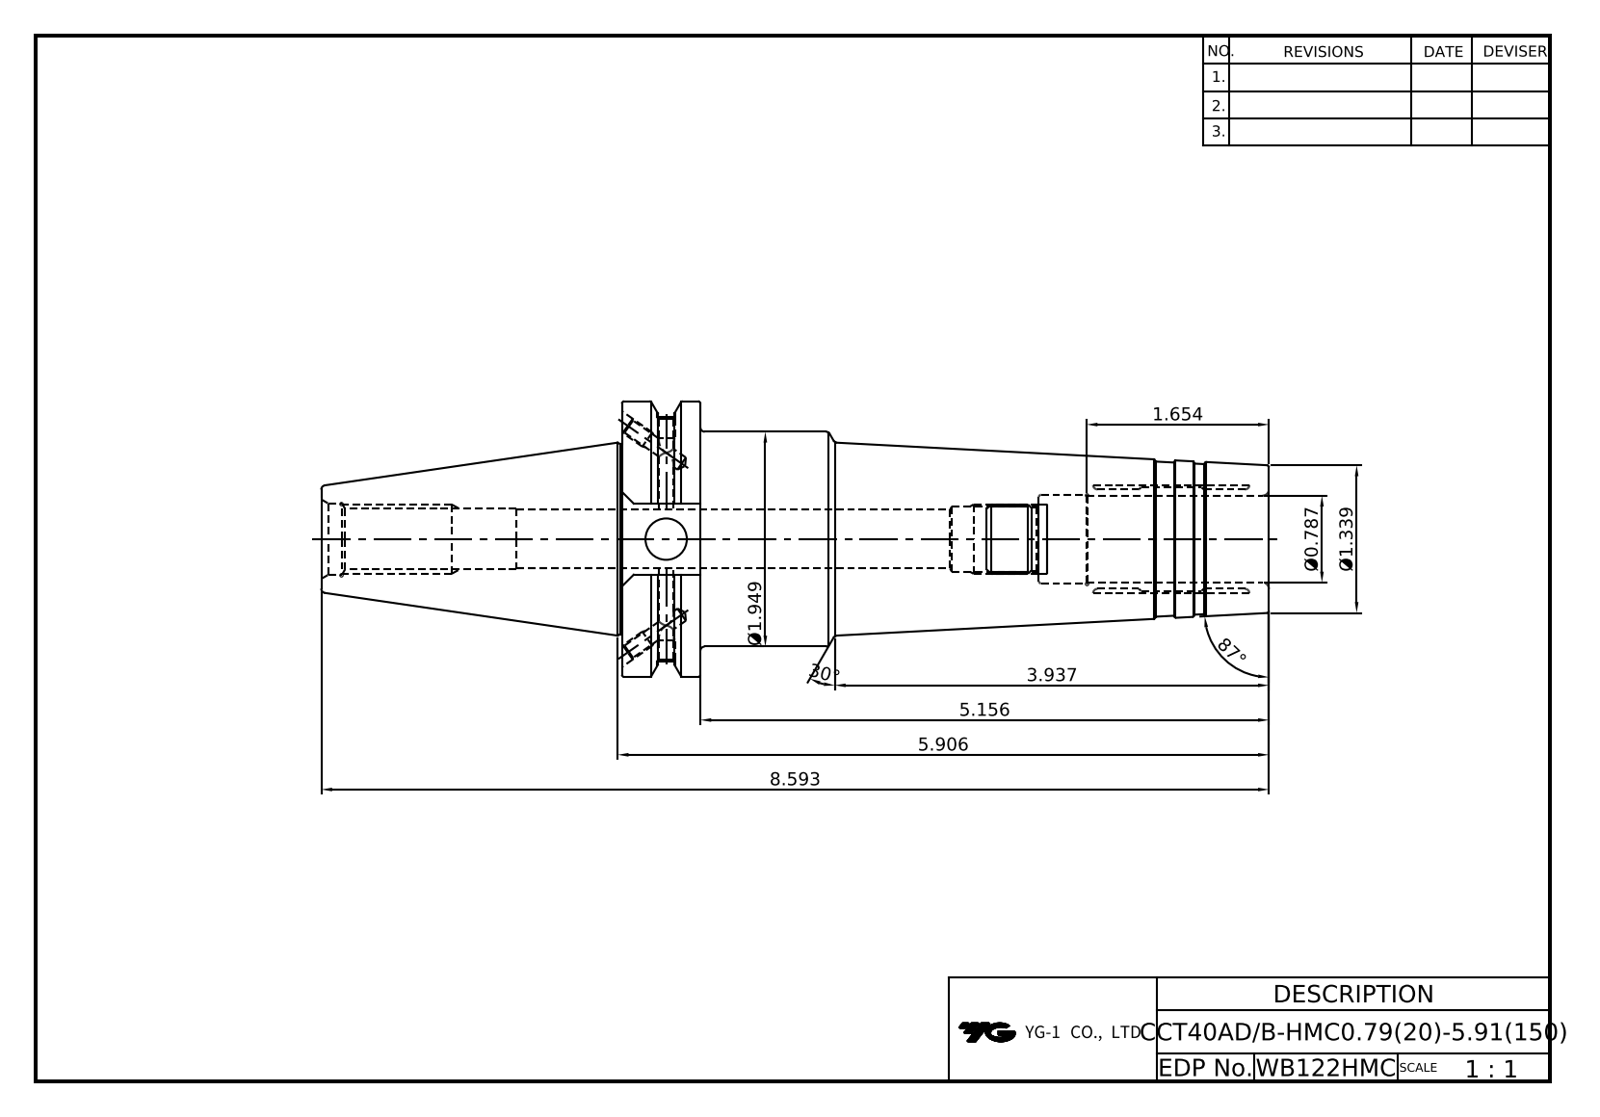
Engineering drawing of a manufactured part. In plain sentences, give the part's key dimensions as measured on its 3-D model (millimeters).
The part is named "LO-CCT40ADB-HMC20-150". Its 3-D file was written by "Autodesk Inventor 2022 (AUTOMOTIVE_DESIGN)". It is 1 solid with 106 faces: 35 planar, 30 cylindrical and 41 other. Overall it measures 218.25 by 63.5 by 61.09 millimeters. Its volume is 256 221 cubic millimeters and its surface area 43 950 square millimeters. Round holes: 4 of diameter 3.24, 2 of diameter 4, 2 of diameter 4.2, 1 of diameter 9.53, 1 of diameter 13, 1 of diameter 13.39, 1 of diameter 14.92, 1 of diameter 16.3, 1 of diameter 20, 1 of diameter 20.6. Round bosses or shafts: 1 of diameter 63.5, 1 of diameter 49.5, 1 of diameter 43.8. Partial cylindrical surfaces (rounded edges, fillets, slot ends): 1 of radius 8.19, 1 of radius 28.15. The main face-to-face distances are 18.05, 149, 130.95, 47.6, 16.38, 96, 77.95, 53, 69.25, 87.3.
